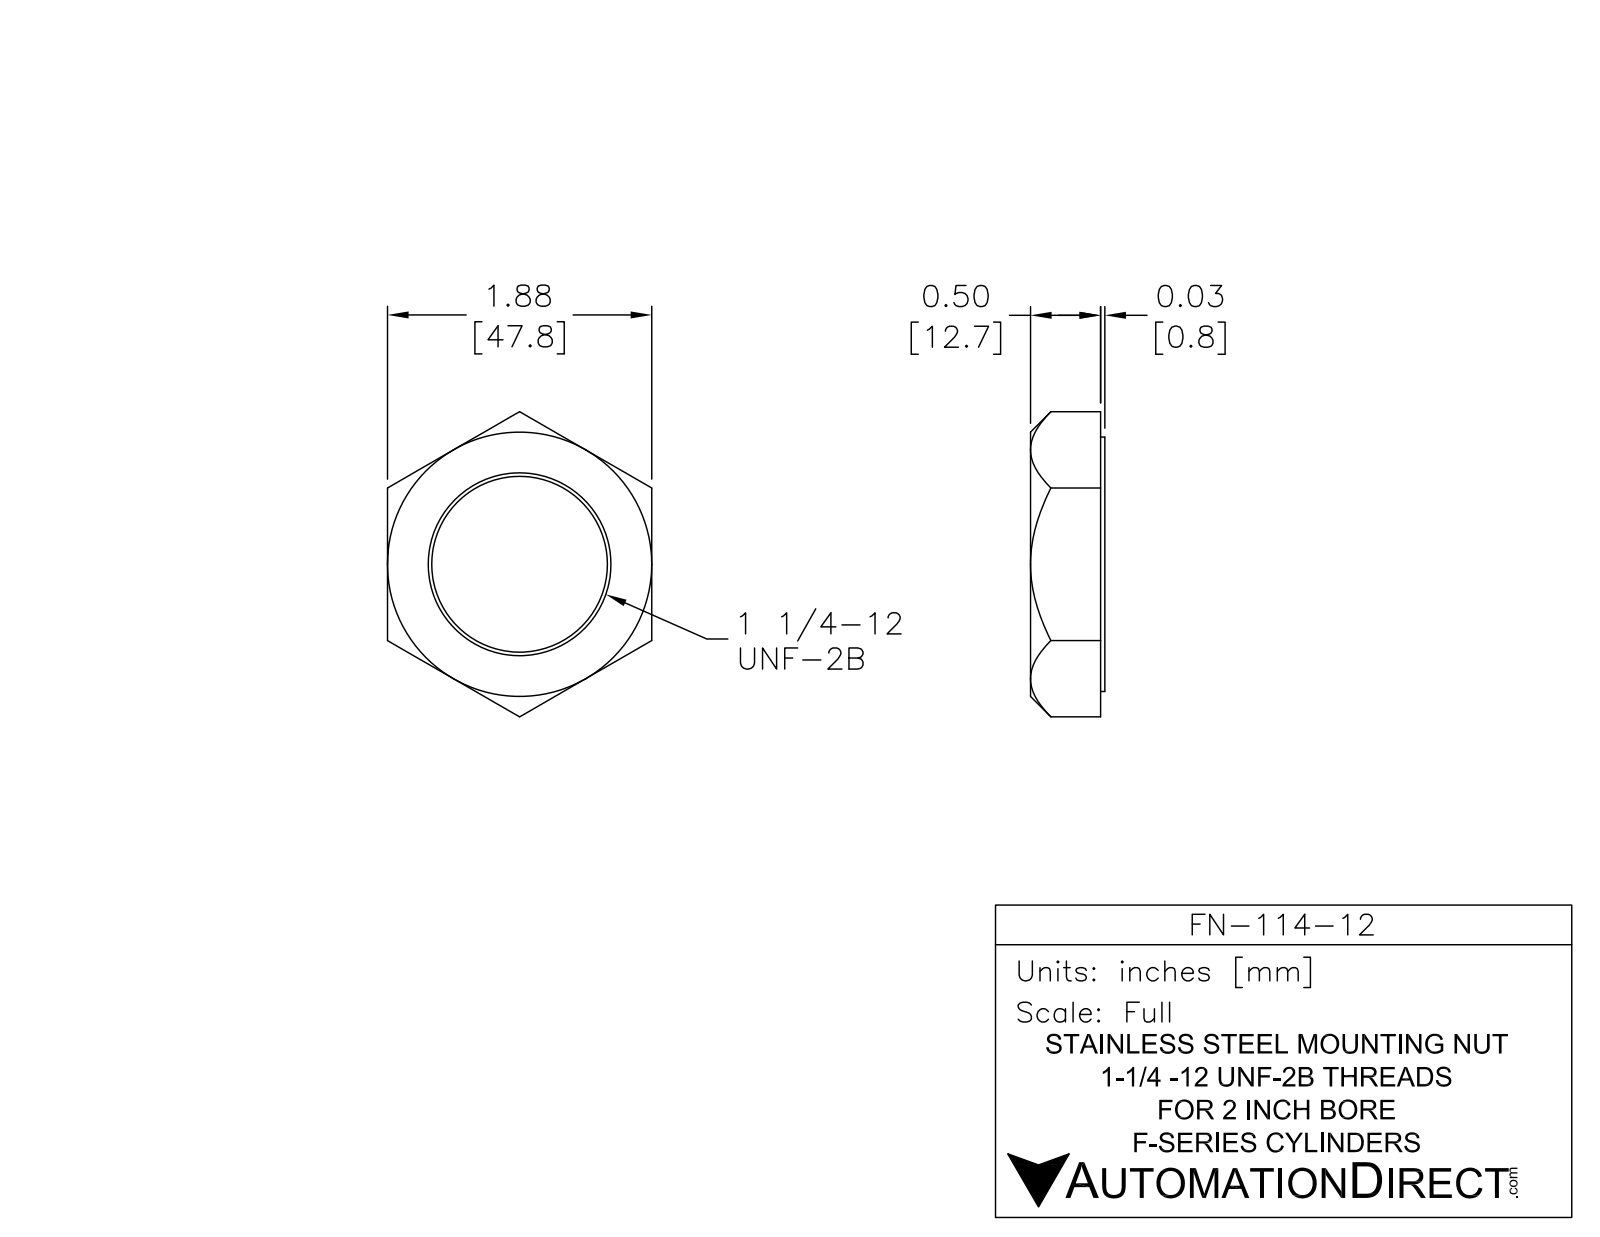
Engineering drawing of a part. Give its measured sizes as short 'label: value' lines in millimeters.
name: FN-114-12
written by: SolidWorks 2017 (AUTOMOTIVE_DESIGN)
unit: mm
bodies: 1 solid, 20 faces (9 planar, 4 cylindrical, 7 other)
size: 55 × 47.6 × 13.5
volume: 16 650 mm³; area: 5 874 mm²
holes: 1× ⌀29.8
bosses: 1× ⌀46
face distances: 13.5, 47.6, 0.8, 12.7
